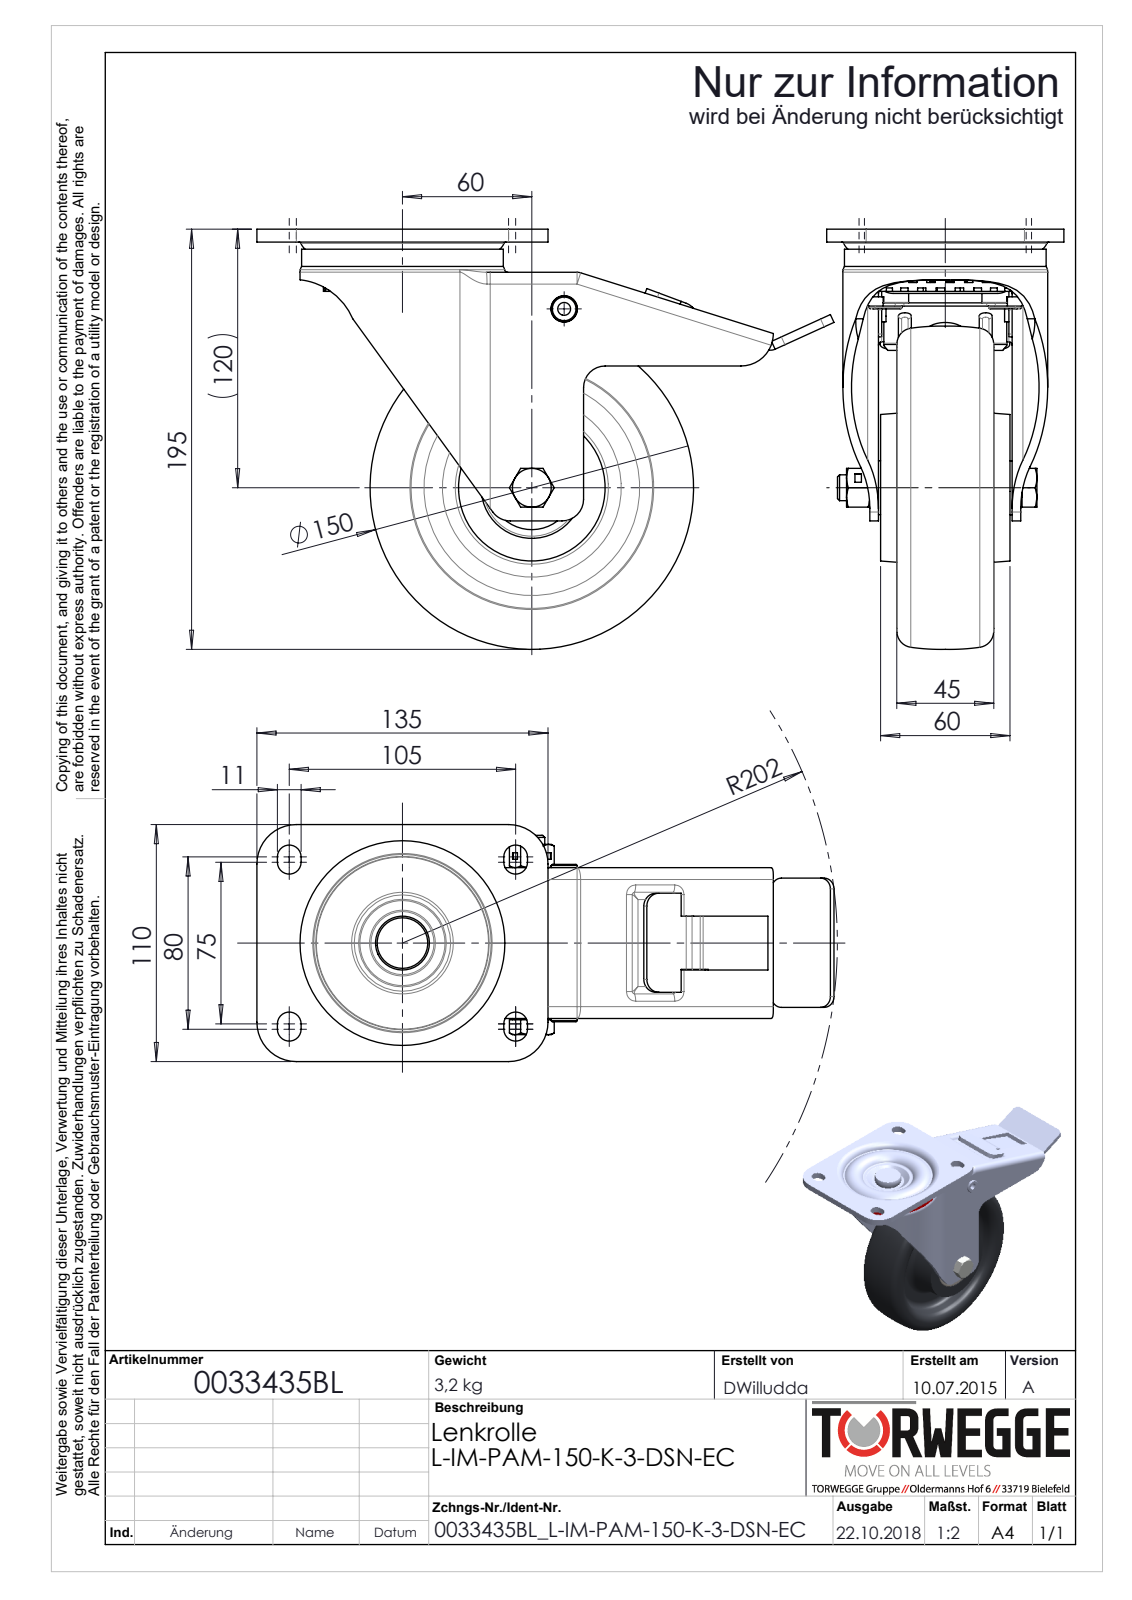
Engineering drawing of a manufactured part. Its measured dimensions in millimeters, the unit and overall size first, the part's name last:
Units: millimetres
Overall size (bounding box): 267.63 × 195.02 × 110
Round holes (diameter × count): ⌀16.2 ×2, ⌀3.6 ×1, ⌀6 ×1, ⌀6.6 ×1, ⌀8 ×1, ⌀9.6 ×1, ⌀10.2 ×1, ⌀11 ×1, ⌀12 ×1, ⌀12.2 ×1, ⌀12.3 ×1, ⌀12.6 ×1
Round bosses / shafts (diameter × count): ⌀18 ×3, ⌀8 ×2, ⌀93.54 ×1, ⌀73.32 ×1, ⌀47 ×1, ⌀28.1 ×1, ⌀25 ×1, ⌀24 ×1
Partial cylindrical surfaces — rounded edges, fillets, slot ends (radius × count): R4 ×16, R1.5 ×15, R5.5 ×13, R5 ×11, R3 ×9, R0.31 ×8, R0.75 ×8, R0.17 ×7
Main face-to-face distances: 4, 66, 1.5, 1, 6, 62, 5, 25, 70, 35
Hole centre spacings: 84.34
Volume: 925 978 mm³ · Surface area: 289 901 mm²
Bodies: 21 solids, 1438 faces (777 planar, 362 cylindrical, 299 other)
Part name (STEP PRODUCT): 0033435BL_L-IM-PAM-150-K-3-DSN-EC
STEP written by: SolidWorks 2016 (AUTOMOTIVE_DESIGN)
